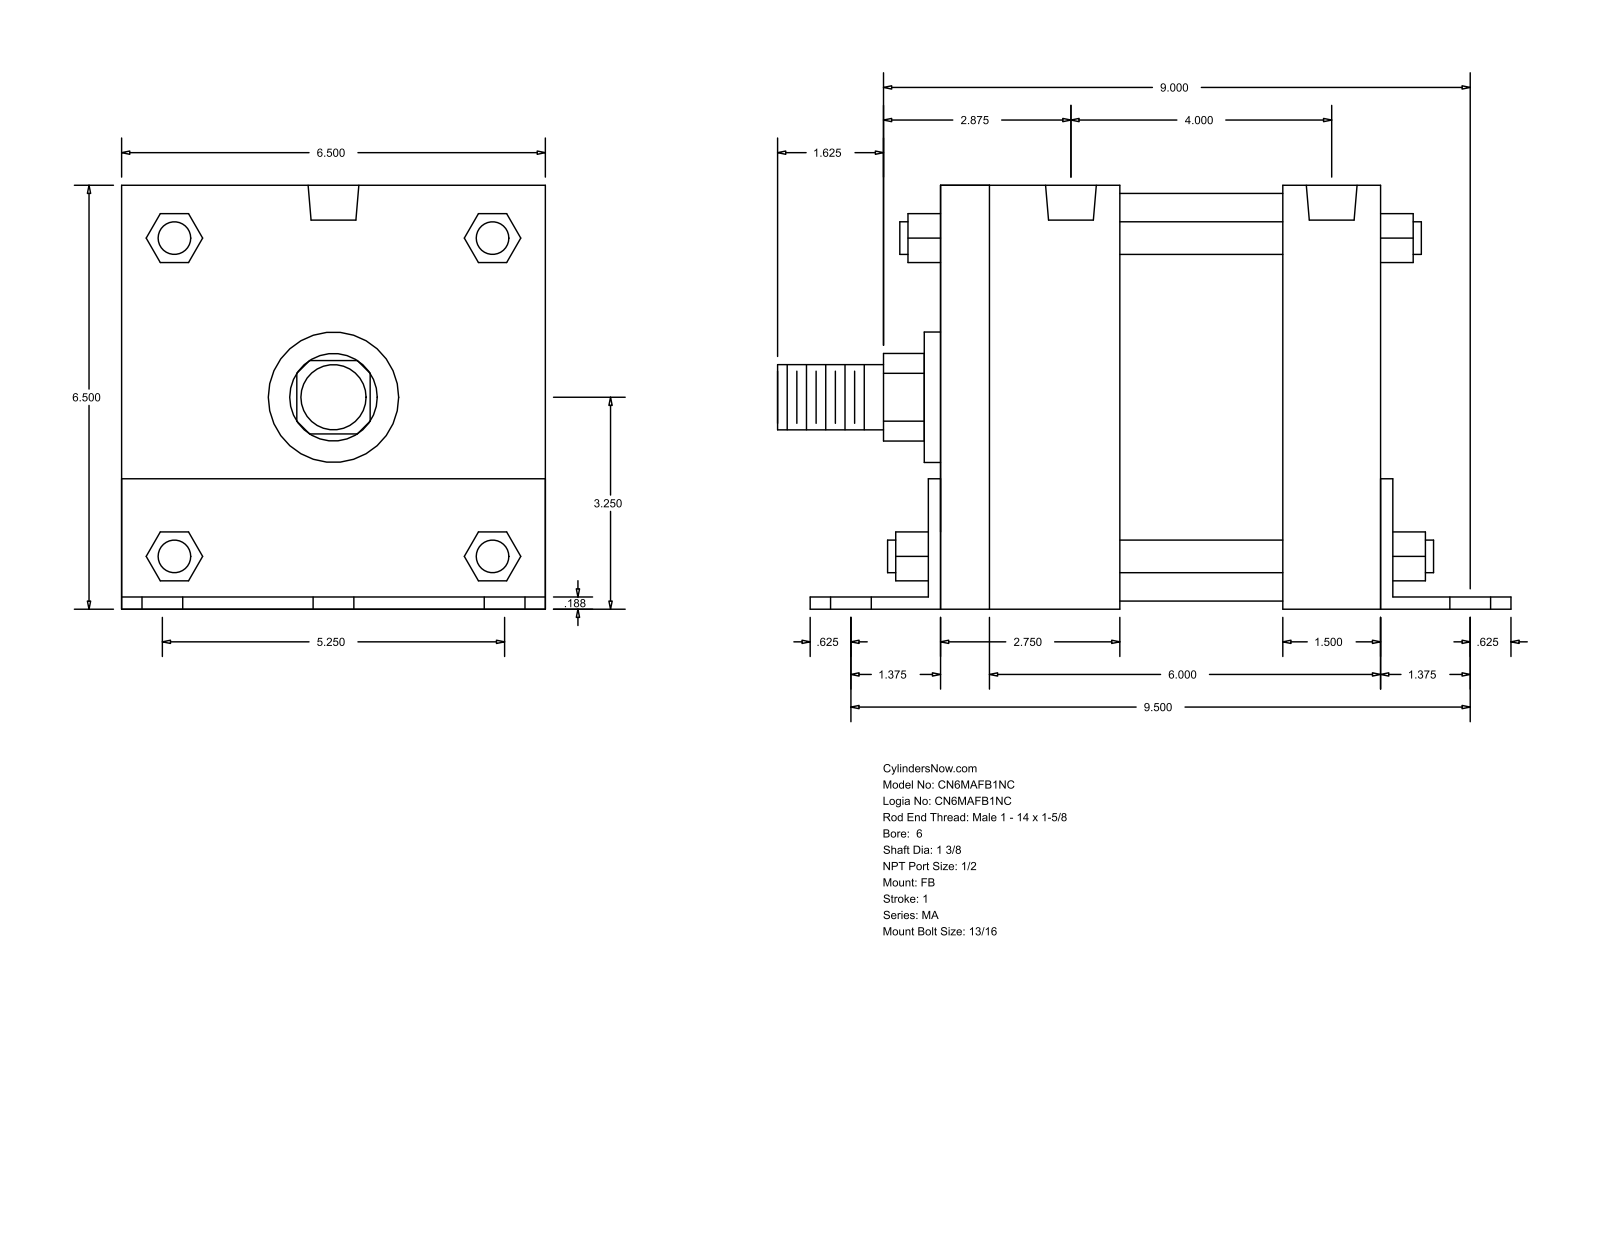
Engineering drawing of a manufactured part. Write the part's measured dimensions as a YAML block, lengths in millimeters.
part_name: "MA_FB__0600_1.375"
step_written_by: "GSSL Pune (CONFIG_CONTROL_DESIGN)"
units: millimeters
bodies: {solids: 0, faces: 140, planar: 105, cylindrical: 35, other: 0}
overall_size: [282.57, 165.15, 165.1]
round_holes:
  - {diameter: 20.64, count: 6}
  - {diameter: 17.46, count: 4}
  - {diameter: 19.77, count: 2}
round_bosses_or_shafts:
  - {diameter: 12.7, count: 4}
  - {diameter: 158.75, count: 1}
  - {diameter: 50.8, count: 1}
  - {diameter: 34.92, count: 1}
  - {diameter: 25.4, count: 1}
partial_cylinders:
  - {radius: 17.06, count: 1}
  - {radius: 32.05, count: 1}
face_to_face_distances: [165.1, 4.76, 168.27, 165.15, 4.71, 160.39, 4.77, 38.1, 42.86, 177.8]
hole_center_spacings: [66.67, 247.29, 238.13, 83.82, 85.78, 98.42, 108.6, 133.34]
